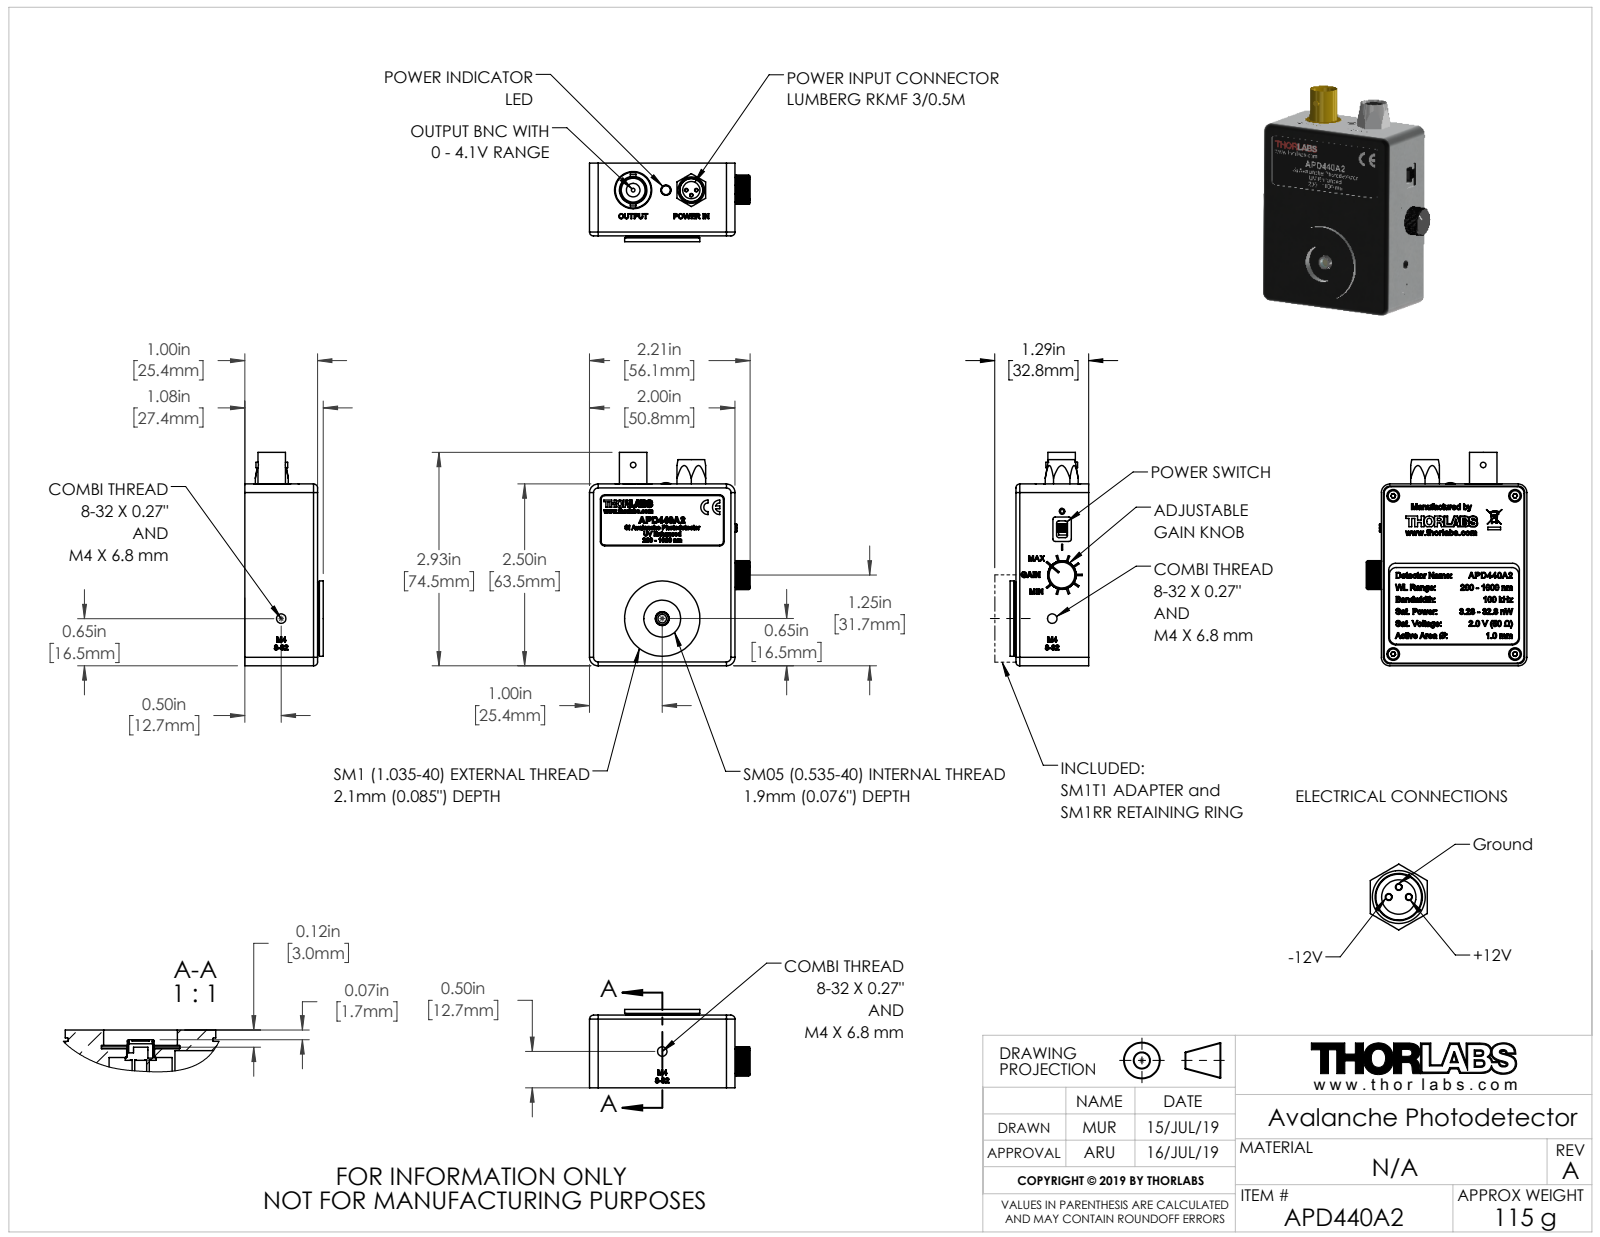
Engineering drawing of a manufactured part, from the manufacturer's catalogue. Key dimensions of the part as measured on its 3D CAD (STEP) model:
Part name (STEP PRODUCT): 19.07.02_APD440A2-Web_Drawing
STEP written by: SolidWorks 2018 (CONFIG_CONTROL_DESIGN)
Units: millimetres
Bodies: 71 solids, 5182 faces (2833 planar, 476 cylindrical, 1873 other)
Overall size (bounding box): 74.54 × 56.08 × 27.4
Volume: 32 132 mm³ · Surface area: 30 296 mm²
Round holes (diameter × count): ⌀1.6 ×9, ⌀1 ×5, ⌀2.4 ×4, ⌀3.3 ×2, ⌀0.39 ×1, ⌀0.9 ×1, ⌀1.27 ×1, ⌀2.2 ×1, ⌀2.5 ×1, ⌀2.92 ×1, ⌀3 ×1, ⌀3.6 ×1
Round bosses / shafts (diameter × count): ⌀2 ×5, ⌀1.57 ×4, ⌀4 ×2, ⌀0.45 ×2, ⌀26.29 ×1, ⌀25.3 ×1, ⌀12.6 ×1, ⌀12.5 ×1
Partial cylindrical surfaces — rounded edges, fillets, slot ends (radius × count): R0.3 ×50, R0.15 ×24, R0.4 ×24, R2.5 ×21, R1 ×12, R3.3 ×10, R0.8 ×8, R2.4 ×8
Main face-to-face distances: 1.58, 2.5, 1.6, 23.8, 23.78, 22.2, 25.38, 48.3, 1.09, 24.87
Hole centre spacings: 4.39, 51.14, 24.61, 24.62, 41.23, 41.24, 42.55, 47.86
